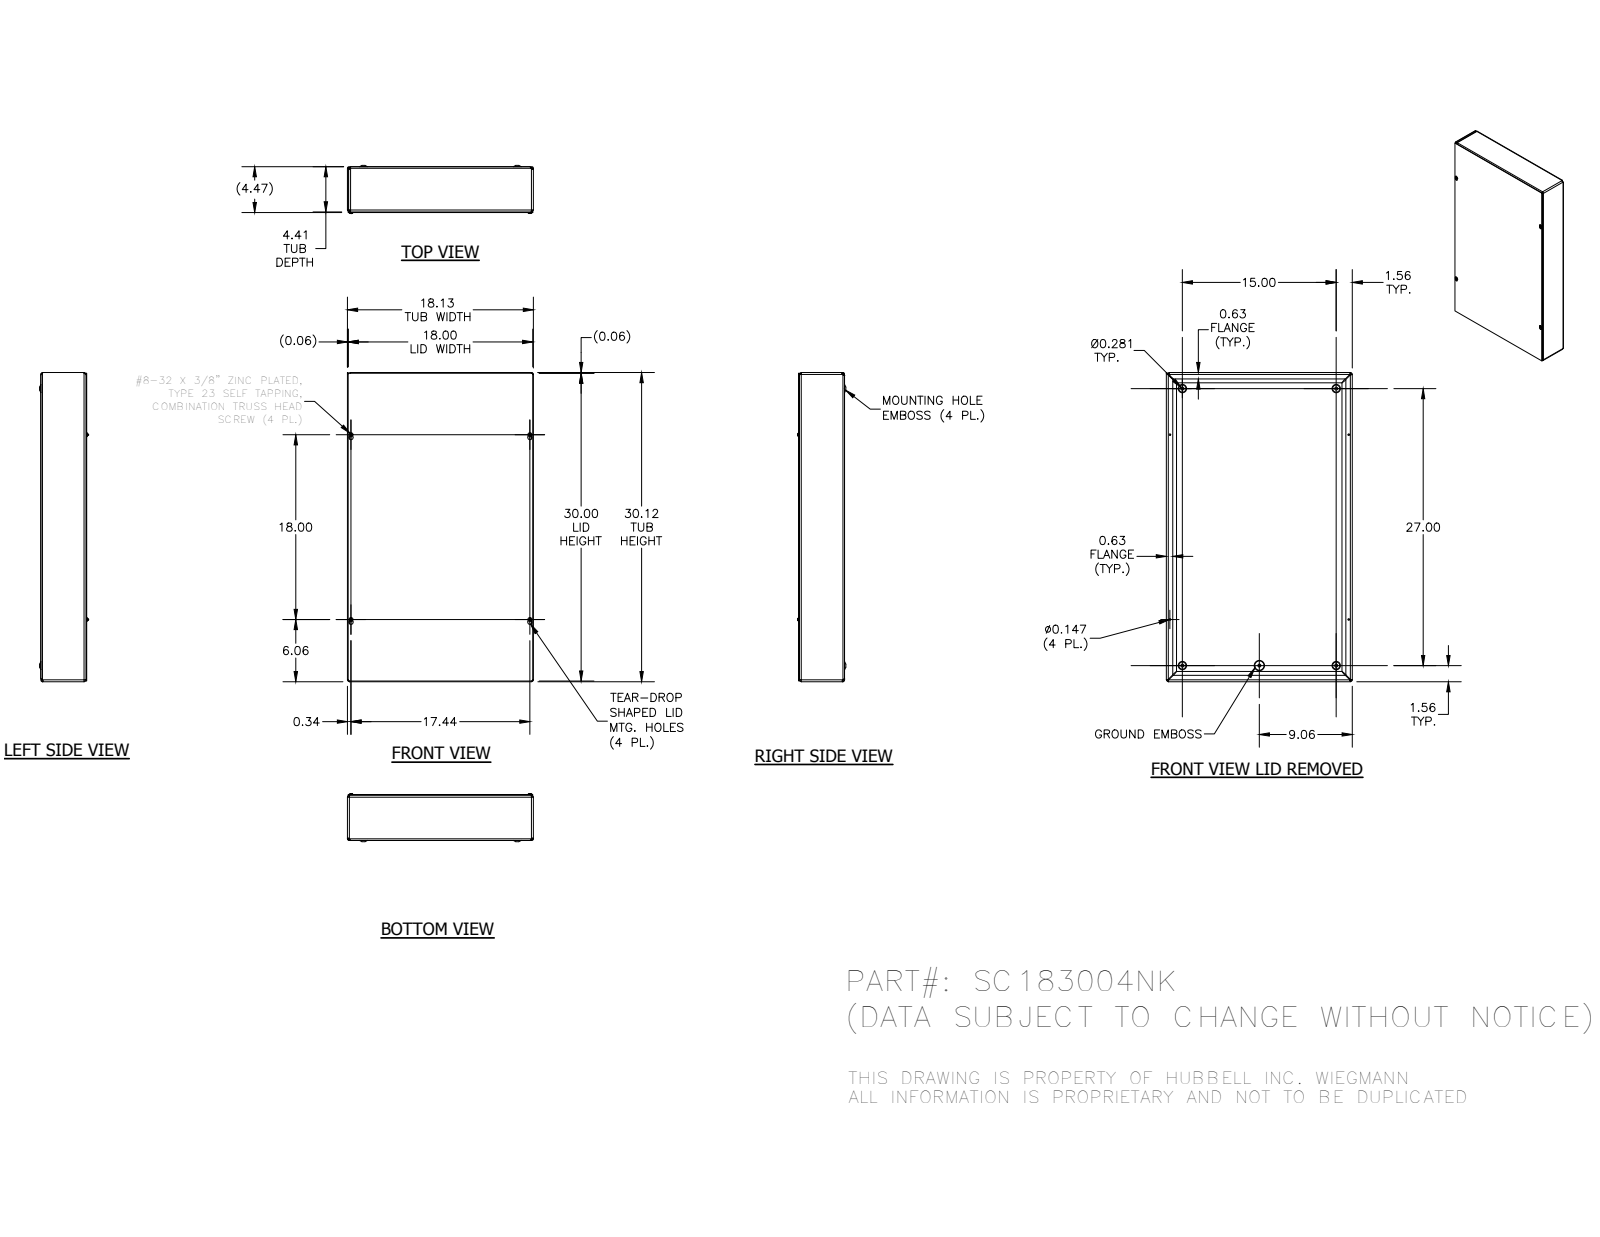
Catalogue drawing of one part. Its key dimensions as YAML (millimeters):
part_name: "SC1830BKP; SC183004NKWRA; SC1830LID; 34056 (+1 more)"
step_written_by: "Autodesk Inventor 2014 (AUTOMOTIVE_DESIGN)"
units: millimeters
bodies: {solids: 7, faces: 357, planar: 132, cylindrical: 67, other: 158}
overall_size: [765.17, 460.38, 119.2]
volume: 1647000
surface_area: 2103000
round_holes:
  - {diameter: 3.73, count: 4}
  - {diameter: 7.62, count: 4}
  - {diameter: 4.19, count: 1}
round_bosses_or_shafts:
  - {diameter: 9.75, count: 4}
  - {diameter: 4.17, count: 4}
  - {diameter: 5.8, count: 1}
partial_cylinders:
  - {radius: 3.17, count: 12}
  - {radius: 4.75, count: 8}
  - {radius: 1.4, count: 4}
  - {radius: 1.57, count: 4}
  - {radius: 2.38, count: 4}
  - {radius: 2.97, count: 4}
  - {radius: 3.15, count: 4}
  - {radius: 3.96, count: 4}
face_to_face_distances: [1.57, 110.32, 111.89, 1.59, 111.91, 113.48, 1.58, 763.6, 460.38, 458.81]
hole_center_spacings: [118.42, 572.34, 704.5, 190.5, 381, 427.51, 427.52, 442.91]
